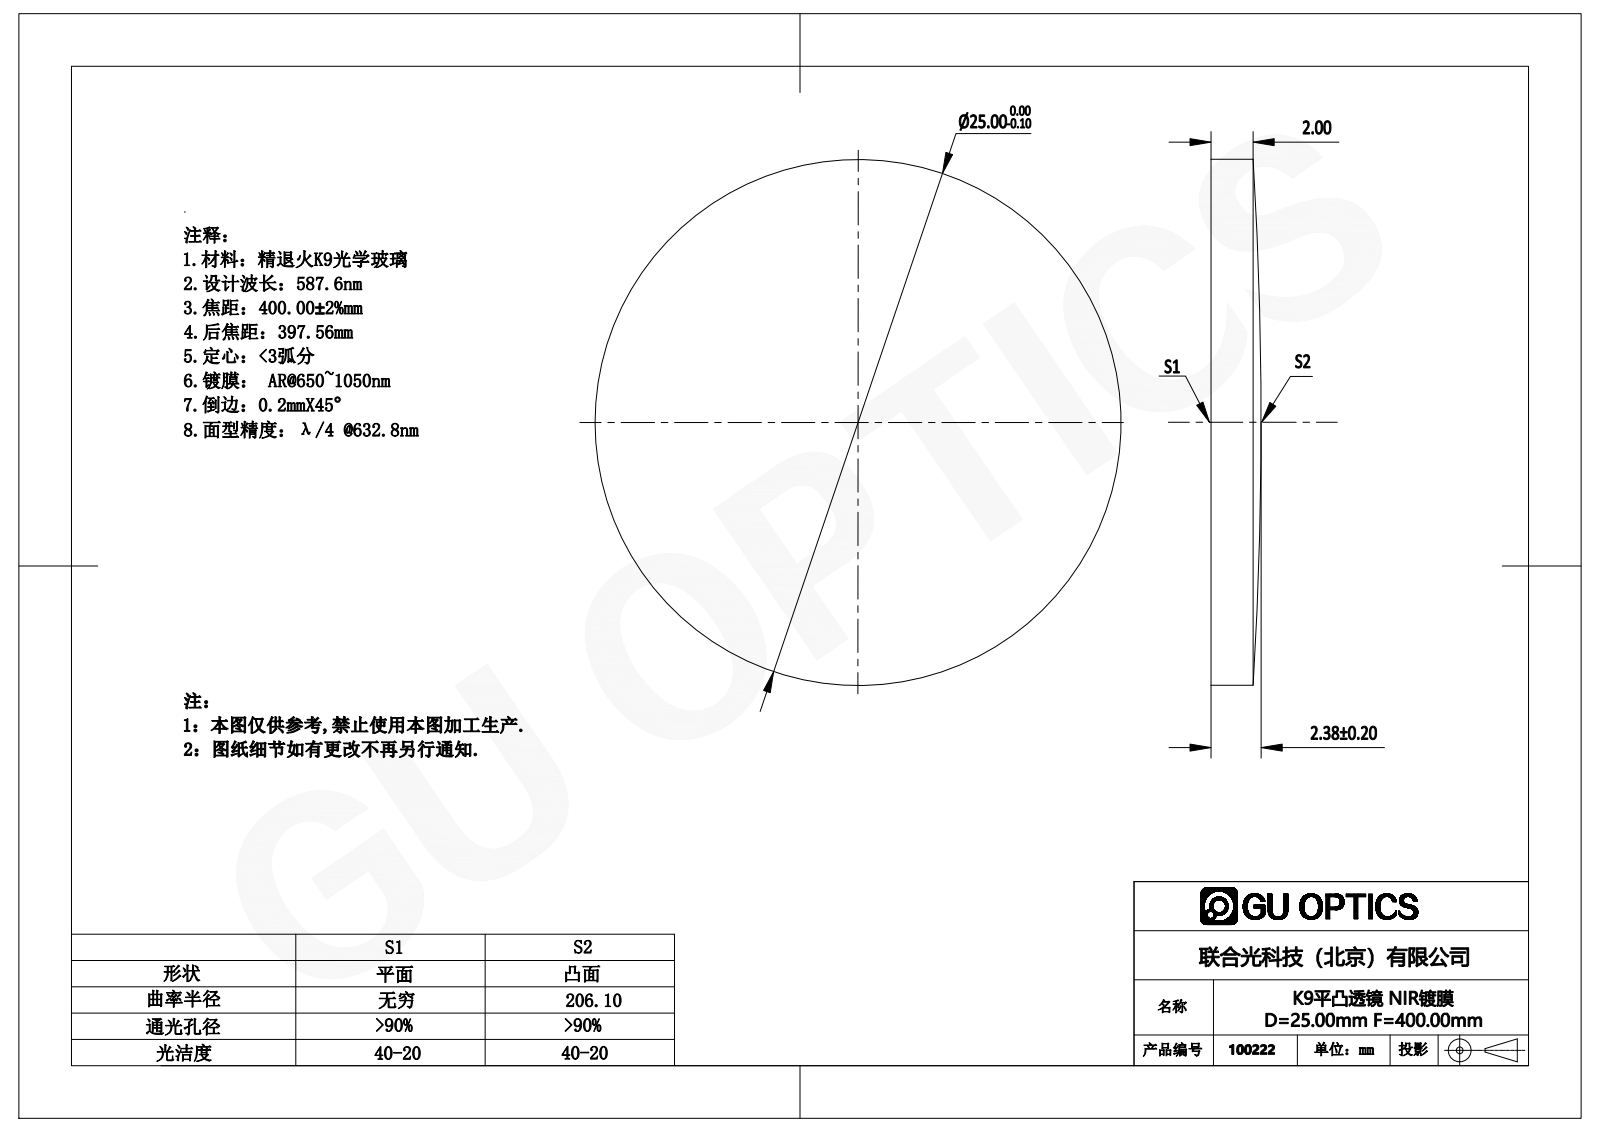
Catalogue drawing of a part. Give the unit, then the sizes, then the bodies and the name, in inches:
Units: inches
Overall size (bounding box): 0.984 × 0.984 × 0.094
Round bosses / shafts (diameter × count): ⌀0.984 ×1
Volume: 0.066 in³ · Surface area: 1.765 in²
Bodies: 1 solid, 5 faces (1 planar, 2 cylindrical, 2 other)
Part name (STEP PRODUCT): 100222
STEP written by: SolidWorks 2016 (AUTOMOTIVE_DESIGN)
